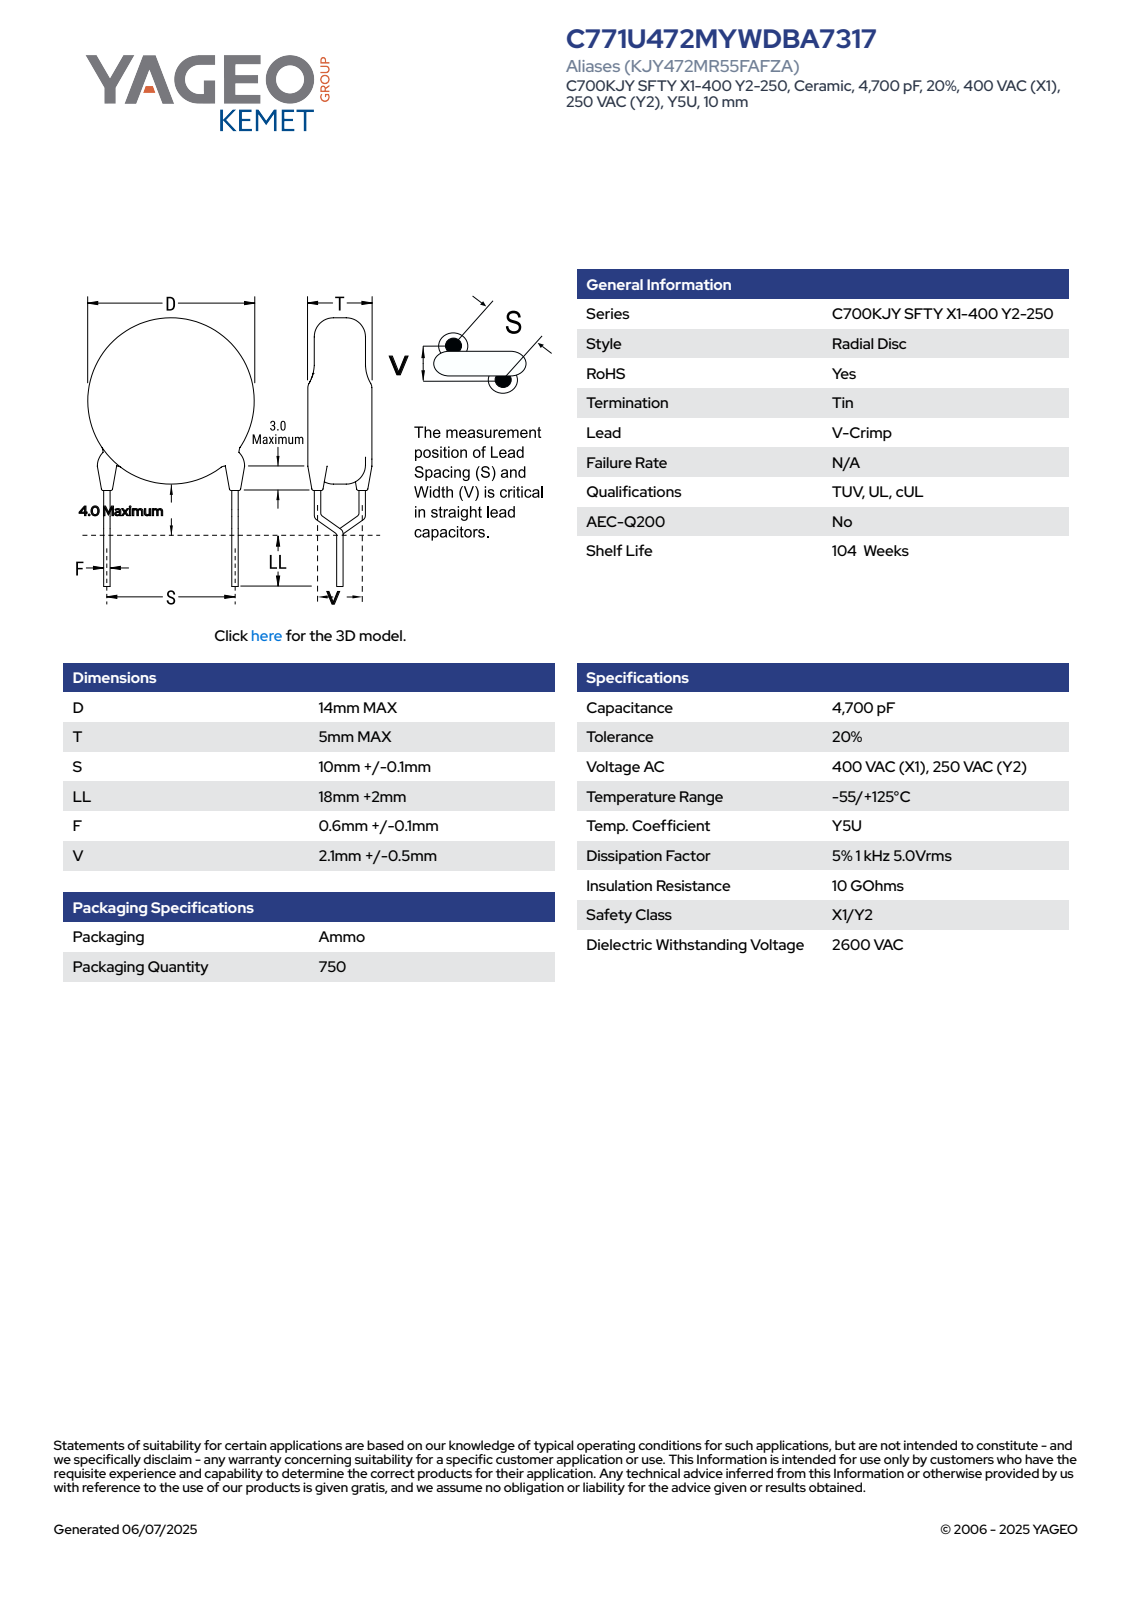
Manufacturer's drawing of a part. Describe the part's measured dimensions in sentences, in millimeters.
The part is named "CCD_VC14X5_D14T5S10LL20F0.7V2.1". Its 3-D file was written by "SolidWorks 2021 (AUTOMOTIVE_DESIGN)". It is 4 solids with 85 faces: 63 planar, 18 cylindrical and 4 other. Overall it measures 34 by 14 by 5 millimeters. Its volume is 772 cubic millimeters and its surface area 617 square millimeters. Round bosses or shafts: 6 of diameter 0.7, 2 of diameter 1.2, 1 of diameter 14. The main face-to-face distances are 5, 20, 28.35, 8.35, 26.41, 6.41, 1.94, 0.53, 7.93, 0.37.
